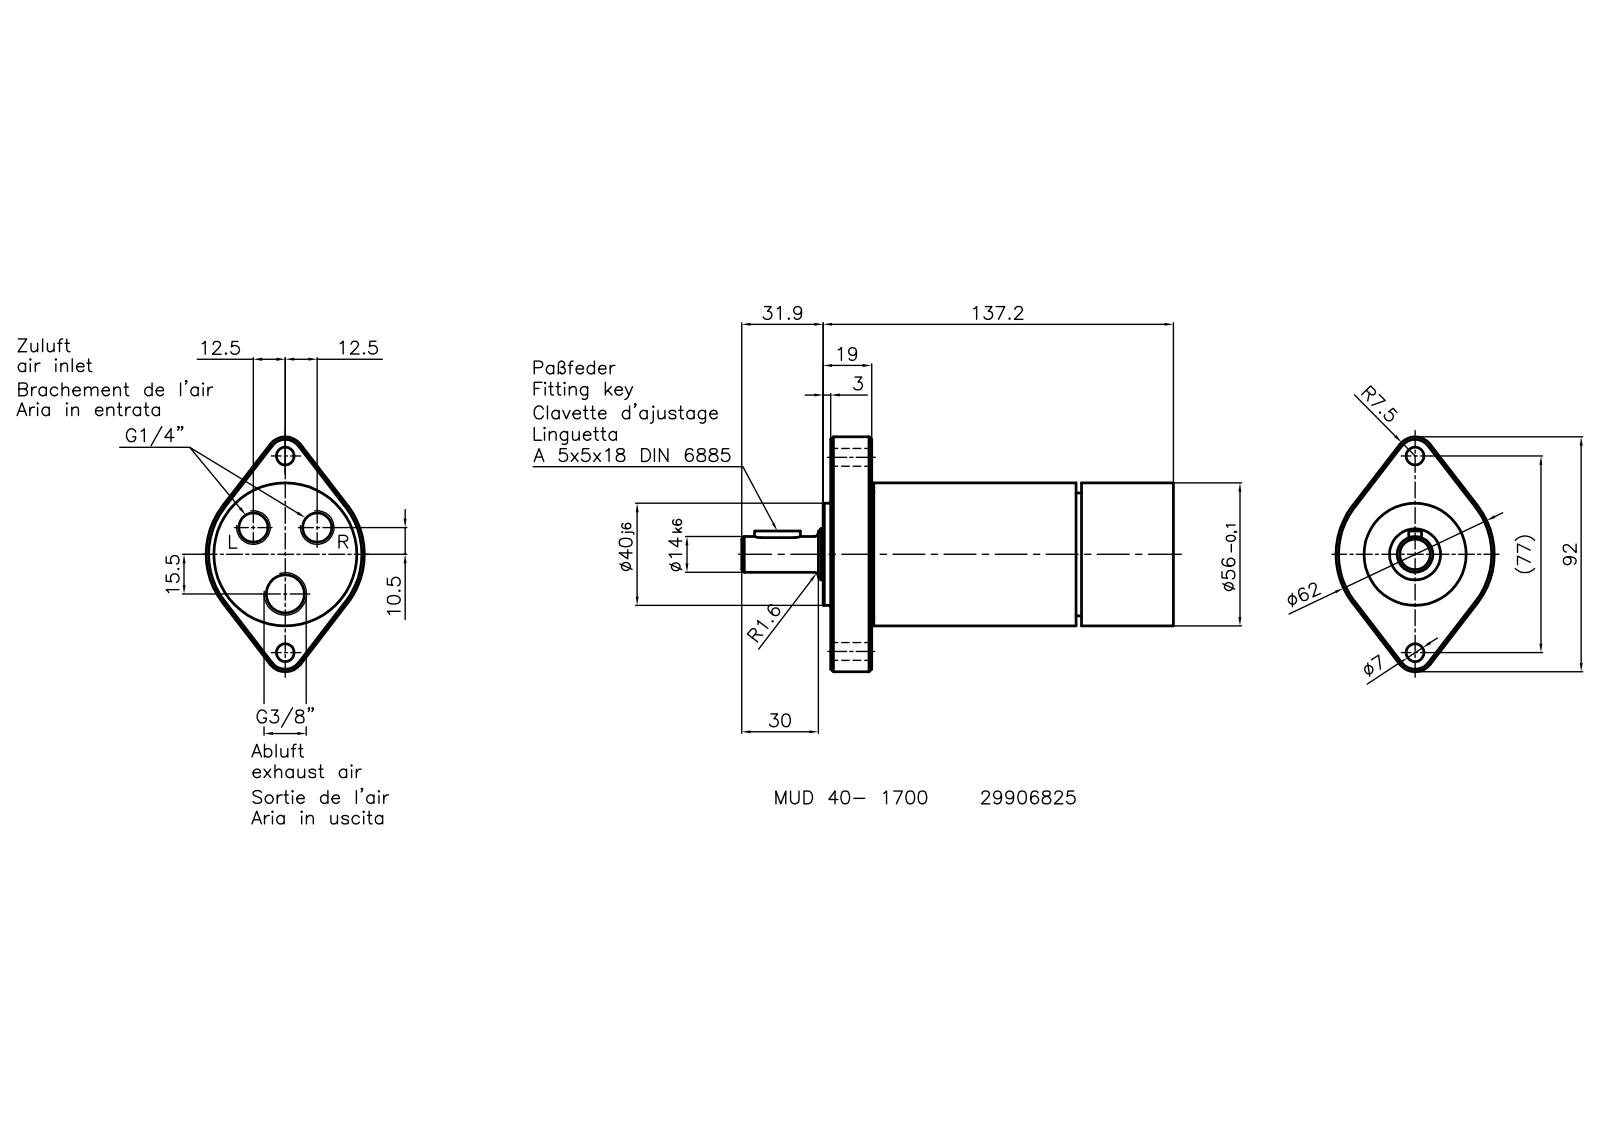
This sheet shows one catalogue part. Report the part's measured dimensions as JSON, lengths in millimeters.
{"part_name": "MUD 40-1700_29906825", "step_written_by": "Autodesk Inventor 2008 (CONFIG_CONTROL_DESIGN)", "units": "millimeters", "bodies": {"solids": 1, "faces": 68, "planar": 29, "cylindrical": 16, "other": 23}, "overall_size": [169.2, 92, 62], "volume_mm3": 351160, "surface_area_mm2": 38117, "round_bosses_or_shafts": [[56, 1], [52.38, 1], [40, 1], [19.95, 1], [14, 1]], "partial_cylinders_radius": [[2.5, 2], [7.5, 2], [11, 1], [23, 1], [31, 1]], "face_to_face_distances": [134.2, 16, 118.2, 3, 19, 137.2, 123.21, 120.21, 104.21, 13.99]}
